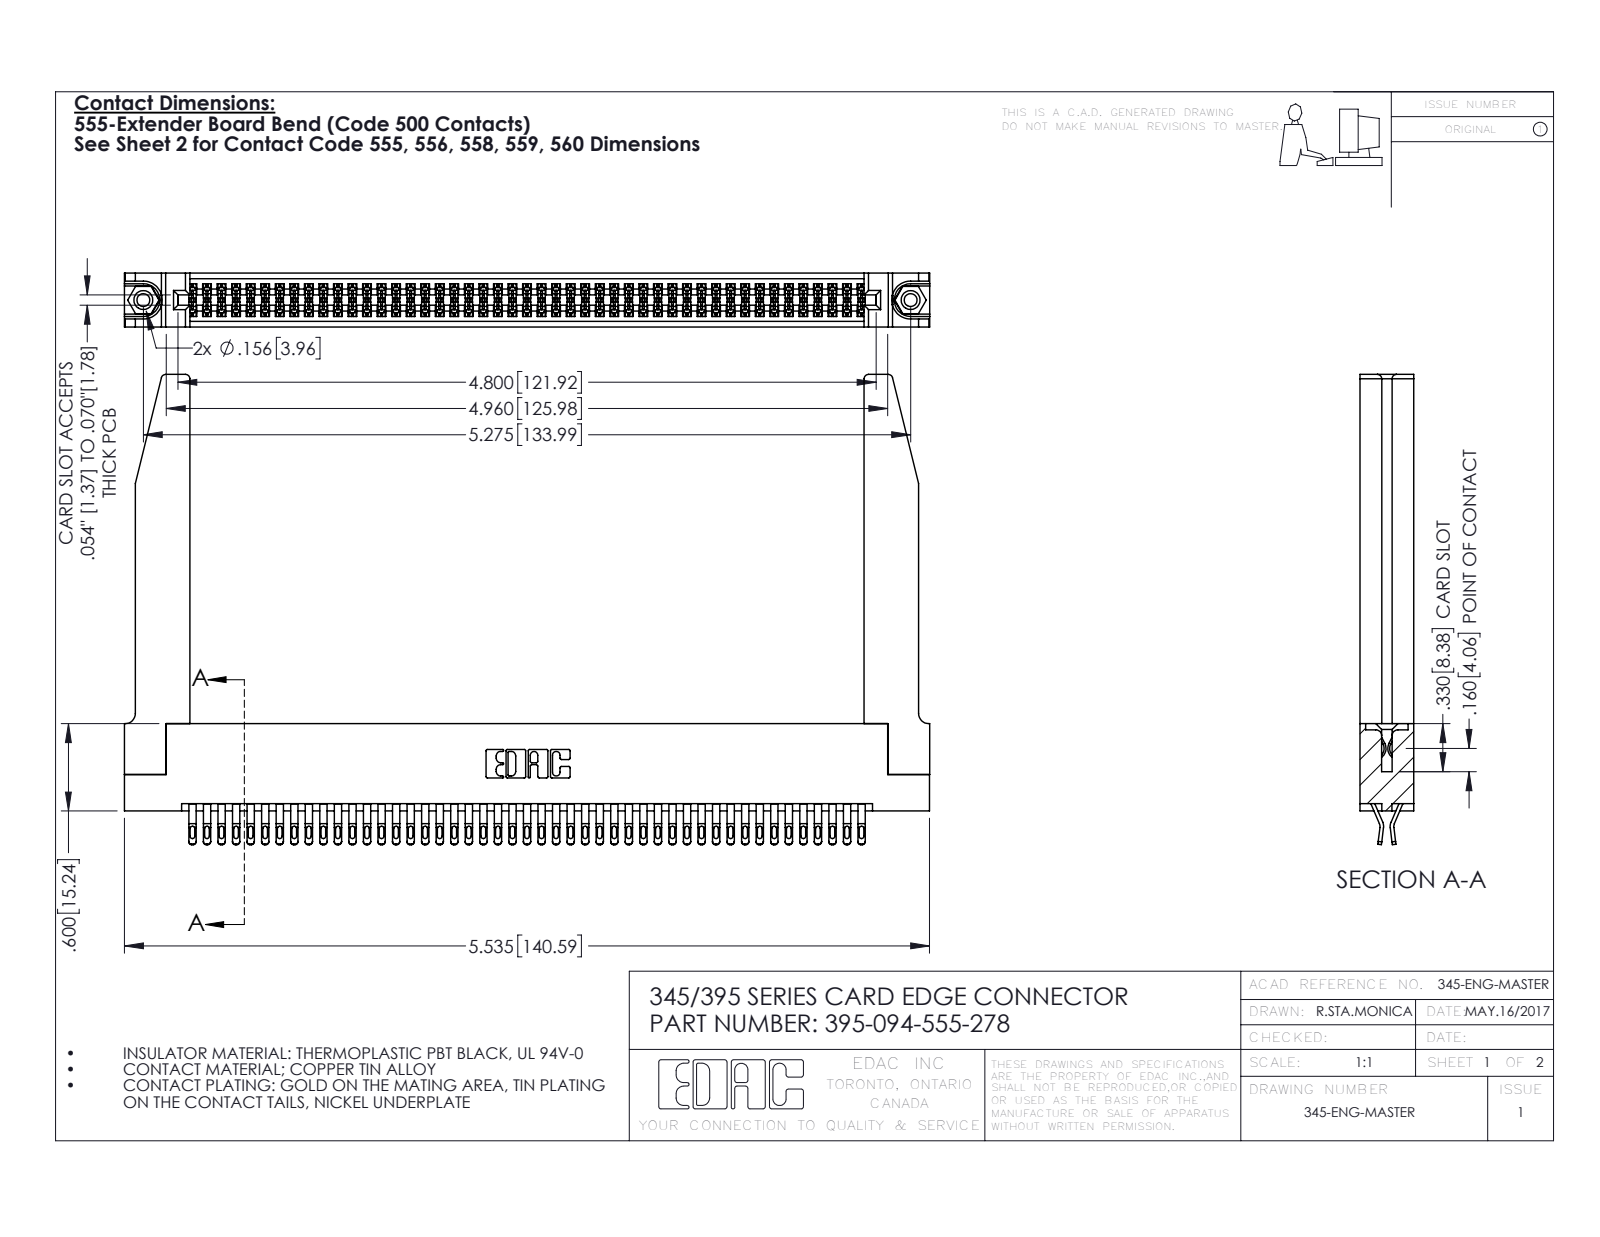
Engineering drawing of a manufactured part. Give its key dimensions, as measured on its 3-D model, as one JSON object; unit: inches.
{"part_name": "345-292-001_555 Tail; 345-220-078_345-220-078; 345 Part_Flush Mounting Lugs - 0.156 Dia-TH; 345-250-001_345-250-001-102 (+1 more)", "step_written_by": "SolidWorks 2016 (CONFIG_CONTROL_DESIGN)", "units": "inches", "bodies": {"solids": 99, "faces": 5624, "planar": 3136, "cylindrical": 2436, "other": 52}, "overall_size": [5.536, 3.232, 0.37], "volume_in3": 1.327, "surface_area_in2": 44.25, "round_holes": [[0.089, 2], [0.125, 2], [0.156, 2], [0.064, 1]], "round_bosses_or_shafts": [[0.155, 2]], "partial_cylinders_radius": [[0.016, 235], [0.02, 188], [0.006, 141], [0.01, 22], [0.03, 8], [0.007, 6], [0.031, 6], [0.026, 3]], "face_to_face_distances": [0.37, 0.072, 0.298, 0.025, 0.2, 0.098, 0.272, 0.225, 0.148, 0.15], "hole_center_spacings": [0.27, 5.039, 5.275]}
